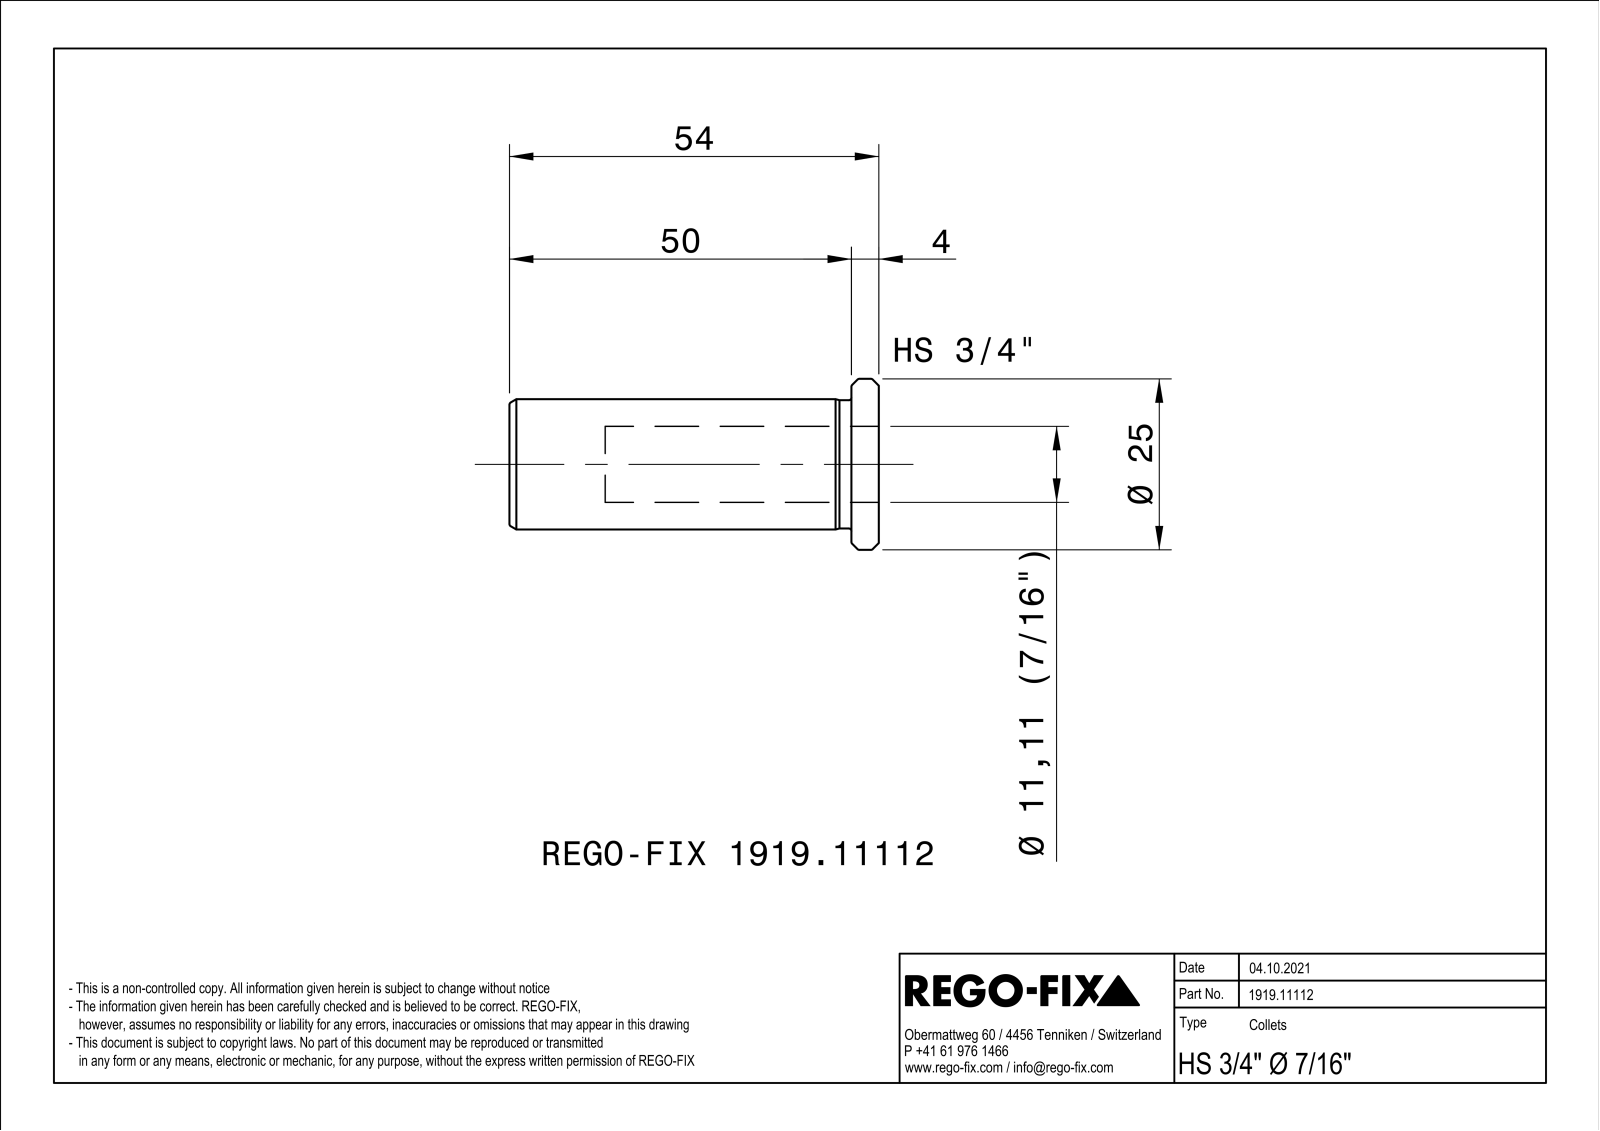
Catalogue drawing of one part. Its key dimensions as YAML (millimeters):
part_name: "NOCUT"
step_written_by: "SIEMENS PLM Software Solid Edge ST10 (AUTOMOTIVE_DESIGN)"
units: millimeters
bodies: {solids: 1, faces: 72, planar: 22, cylindrical: 12, other: 38}
overall_size: [54, 24.98, 24.98]
volume: 8869
surface_area: 6992
round_holes:
  - {diameter: 11.11, count: 1}
  - {diameter: 11.5, count: 1}
  - {diameter: 16.5, count: 1}
round_bosses_or_shafts:
  - {diameter: 25, count: 1}
  - {diameter: 19.05, count: 1}
  - {diameter: 18.75, count: 1}
face_to_face_distances: [1, 4, 54, 50]
